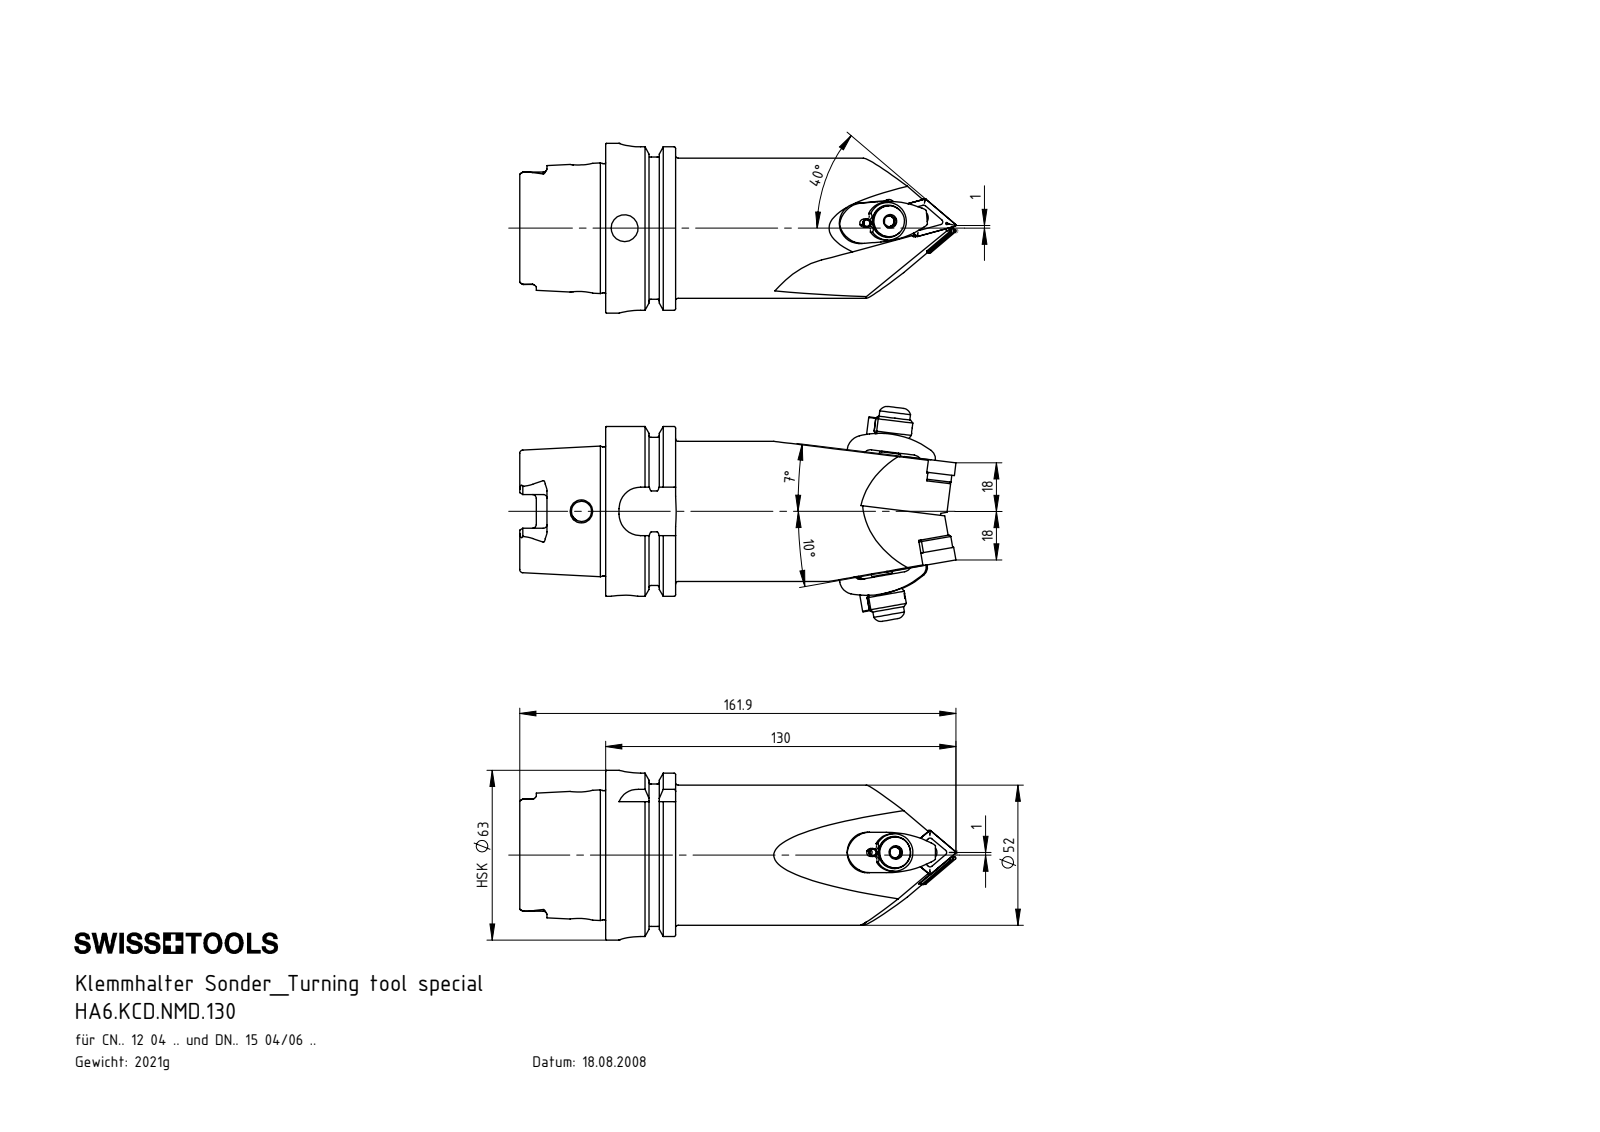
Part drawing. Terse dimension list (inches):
name: WCC-ER3.102.024_C; WCC-ER2.001.010_A; WDF-ER2.101.004_A; WCC-ER5.102.005_A (+8 more)
written by: SolidWorks 2017 (AUTOMOTIVE_DESIGN)
unit: in
bodies: 17 solids, 675 faces (193 planar, 227 cylindrical, 255 other)
size: 6.374 × 3.141 × 2.48
volume: 15.62 in³; area: 77.39 in²
holes: 6× ⌀0.079, 4× ⌀0.276, 3× ⌀0.165, 2× ⌀0.094, 2× ⌀0.118, 2× ⌀0.197, 2× ⌀0.203, 2× ⌀0.244, 2× ⌀0.335, 1× ⌀0.256, 1× ⌀0.258, 1× ⌀0.295
bosses: 4× ⌀0.118, 2× ⌀0.551, 2× ⌀0.453, 2× ⌀0.276, 2× ⌀0.268, 2× ⌀0.244, 2× ⌀0.236, 2× ⌀0.197
rounds: 12× R0.015, 12× R0.027, 8× R0.016, 6× R0.055, 6× R0.059, 4× R0.039, 4× R0.079, 4× R0.118
face distances: 0.63, 1.022, 0.392, 0.187, 0.698, 0.051, 1.256, 1.648, 2.278, 0.176
hole spacings: 0.315, 0.315, 0.323, 0.591, 0.906, 0.566, 0.583, 0.591
